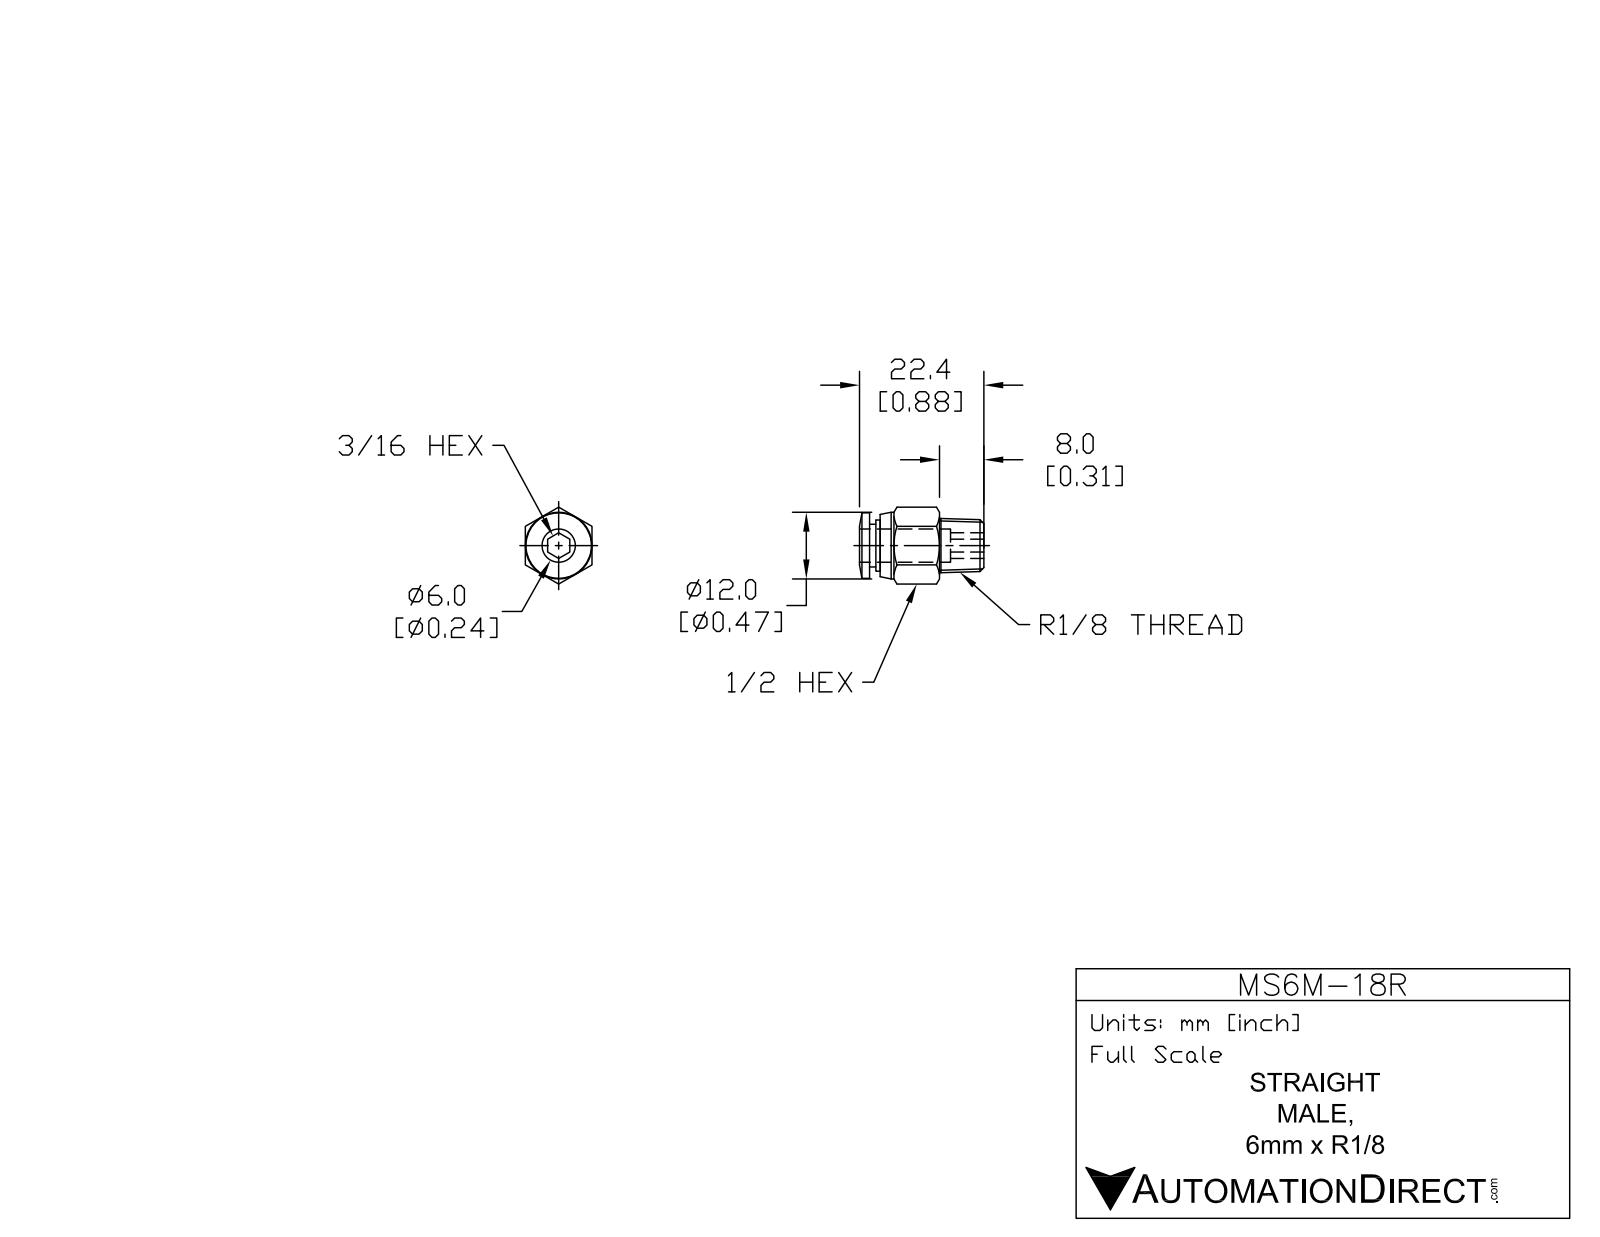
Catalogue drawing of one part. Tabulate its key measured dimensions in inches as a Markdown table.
| quantity | value |
| --- | --- |
| part name | MS6M-18R |
| STEP written by | SolidWorks 2015 (AUTOMOTIVE_DESIGN) |
| units | inches |
| bodies | 1 solid, 49 faces (13 planar, 12 cylindrical, 24 other) |
| overall size | 0.921 × 0.546 × 0.472 |
| volume | 0.099 in³ |
| surface area | 2.387 in² |
| round holes (diameter × count) | 0.197 × 1, 0.248 × 1 |
| round bosses / shafts (diameter × count) | 0.472 × 1, 0.465 × 1, 0.362 × 1, 0.303 × 1 |
| main face-to-face distances | 0.472, 0.535, 0.461, 0.075, 0.315, 0.776, 0.85, 0.805, 0.49, 0.03 |
